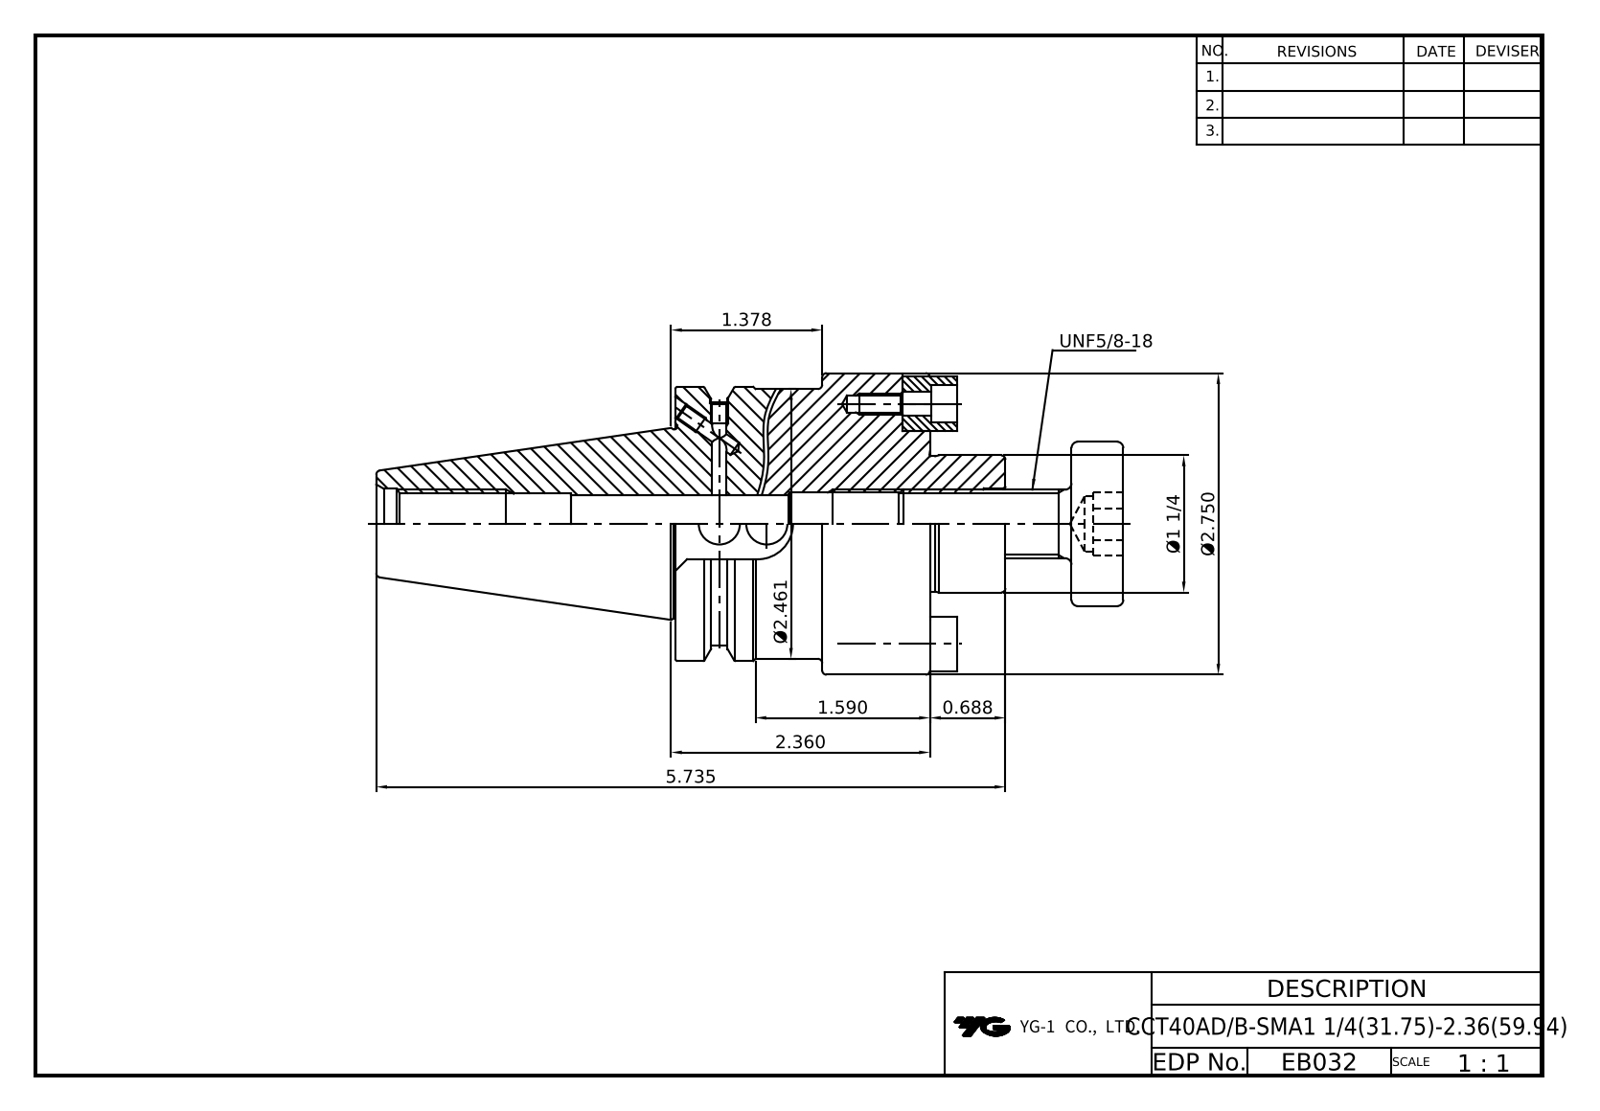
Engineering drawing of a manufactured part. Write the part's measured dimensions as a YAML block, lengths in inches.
part_name: "LO-CCT40ADB-SMA31.75-59.944; DRIVE KEY-12.7x12.7x12.7; HEX'' WRENCH BOLT-UNC#10-24x1_2L; COLLAR BOLT-UNF5_8-18x40L"
step_written_by: "Autodesk Inventor 2022 (AUTOMOTIVE_DESIGN)"
units: inches
bodies: {solids: 6, faces: 185, planar: 90, cylindrical: 50, other: 45}
overall_size: [6.601, 2.75, 2.75]
volume: 16.59
surface_area: 70.35
round_holes:
  - {diameter: 0.128, count: 4}
  - {diameter: 0.145, count: 2}
  - {diameter: 0.157, count: 2}
  - {diameter: 0.165, count: 2}
  - {diameter: 0.217, count: 2}
  - {diameter: 0.343, count: 2}
  - {diameter: 0.375, count: 1}
  - {diameter: 0.5, count: 1}
  - {diameter: 0.512, count: 1}
  - {diameter: 0.527, count: 1}
  - {diameter: 0.565, count: 1}
  - {diameter: 0.642, count: 1}
round_bosses_or_shafts:
  - {diameter: 0.312, count: 2}
  - {diameter: 0.19, count: 2}
  - {diameter: 2.75, count: 1}
  - {diameter: 2.5, count: 1}
  - {diameter: 2.461, count: 1}
  - {diameter: 1.724, count: 1}
  - {diameter: 1.5, count: 1}
  - {diameter: 1.25, count: 1}
partial_cylinders:
  - {radius: 0.25, count: 2}
  - {radius: 0.322, count: 1}
  - {radius: 1.108, count: 1}
face_to_face_distances: [2.32, 3.875, 1.554, 3.402, 1.082, 0.472, 0.25, 0.5, 2.07, 1.332]
hole_center_spacings: [1.093, 1.094, 2.187, 2.187, 2.187]
